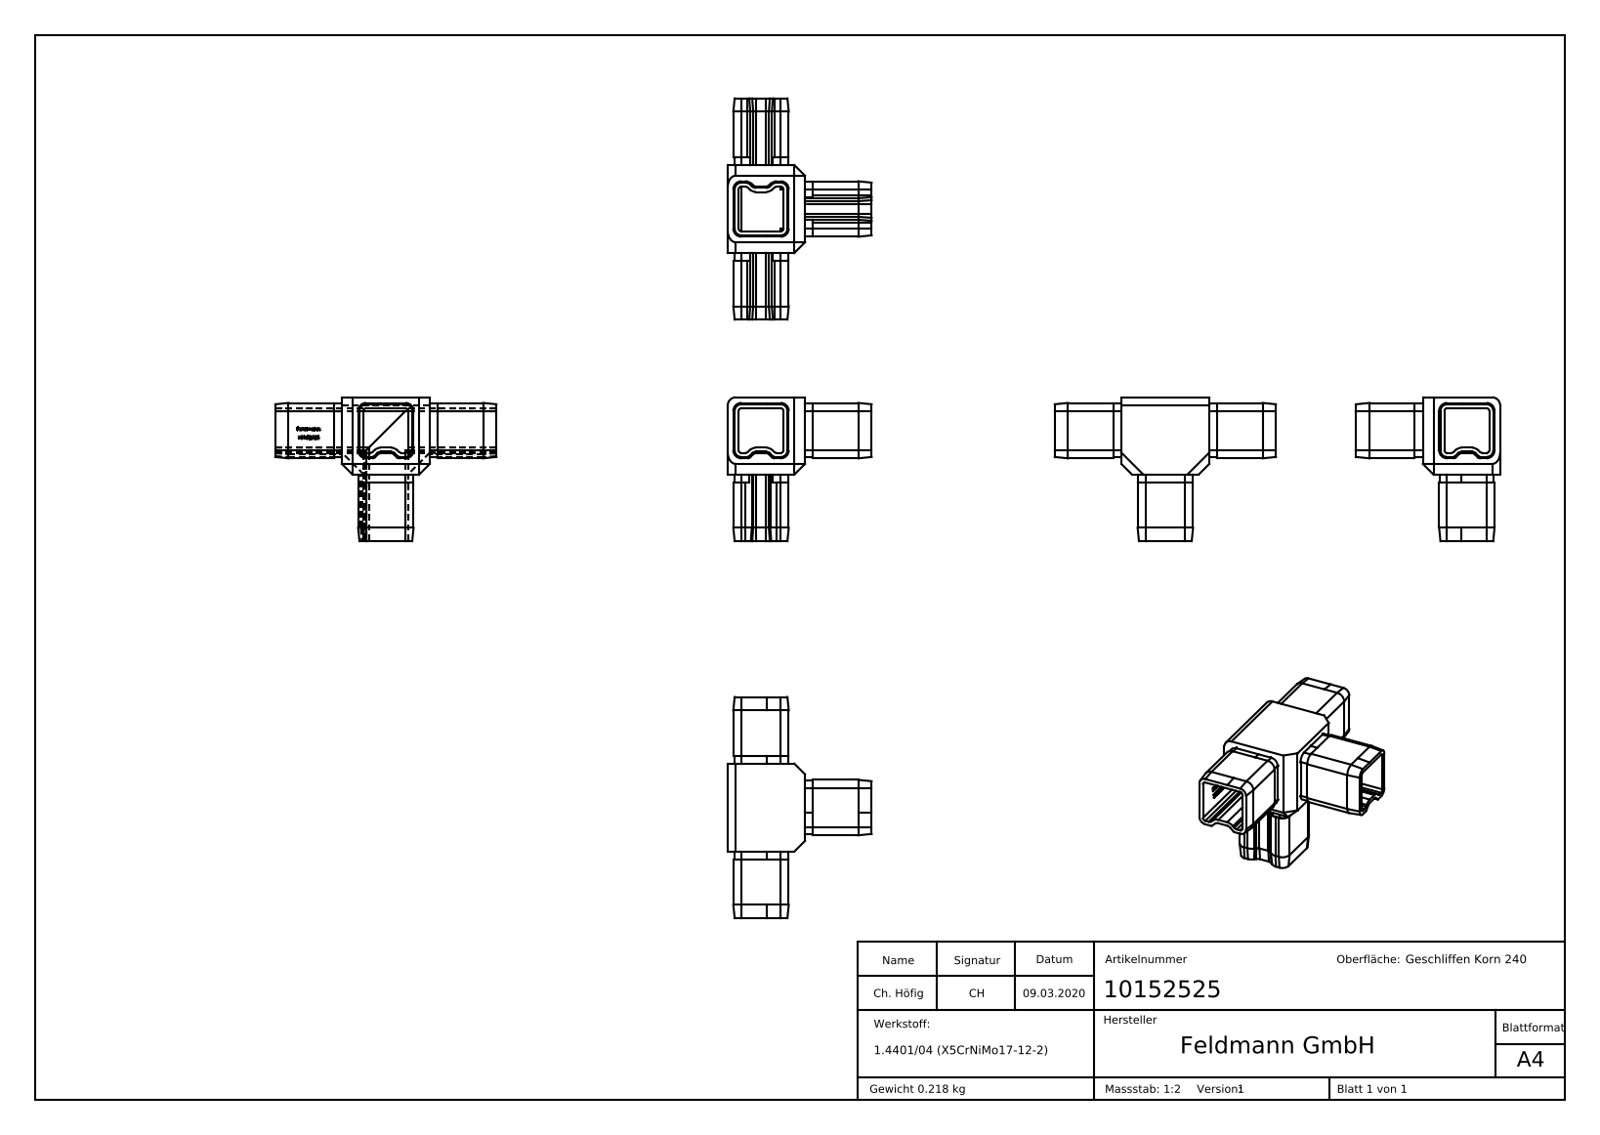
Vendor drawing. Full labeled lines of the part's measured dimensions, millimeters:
Part name (STEP PRODUCT): 10152525
STEP written by: SolidWorks 2015 (CONFIG_CONTROL_DESIGN)
Units: millimetres
Bodies: 1 solid, 501 faces (294 planar, 82 cylindrical, 125 other)
Overall size (bounding box): 83 × 54 × 54
Volume: 27 273 mm³ · Surface area: 21 360 mm²
Partial cylindrical surfaces — rounded edges, fillets, slot ends (radius × count): R1.5 ×16, R3 ×15, R1 ×12, R2.7 ×12, R3.5 ×8
Main face-to-face distances: 2, 16.8, 18.8, 4.1, 2.1, 20.9, 20.8, 22.9, 26.9, 24.9
